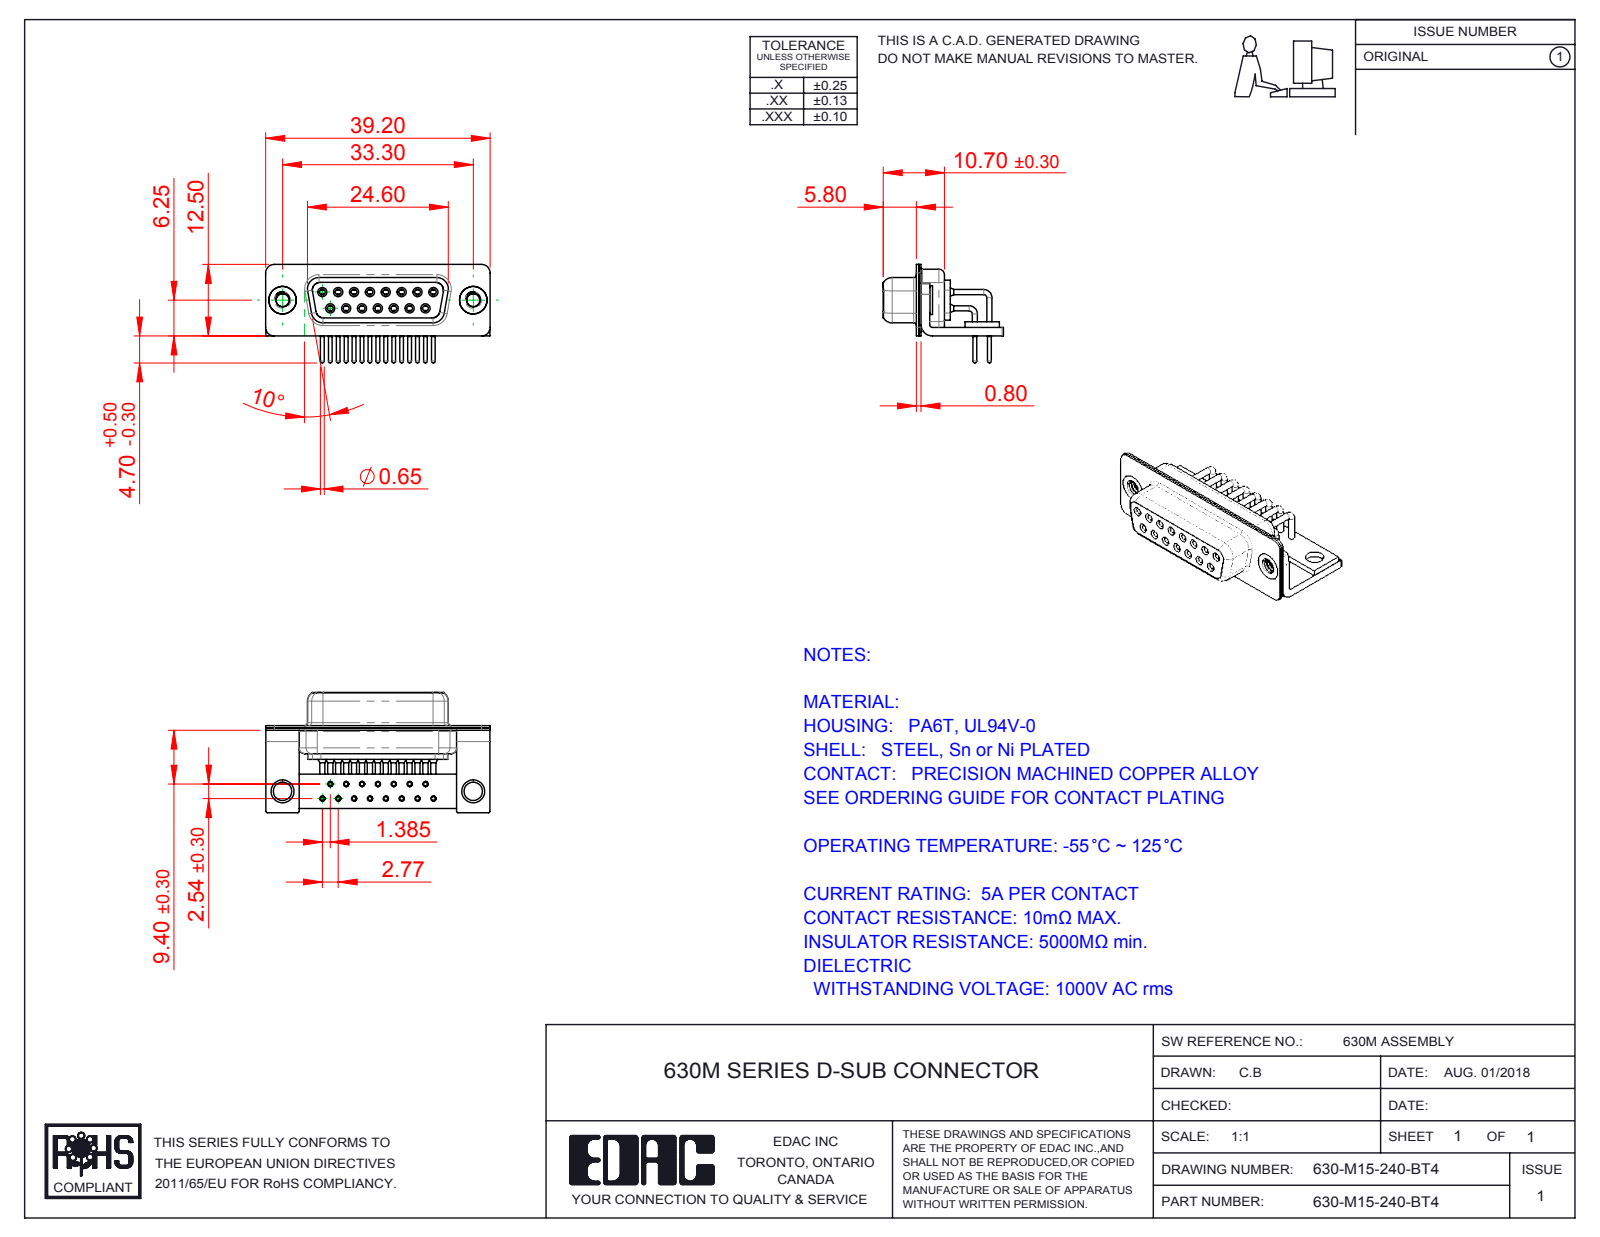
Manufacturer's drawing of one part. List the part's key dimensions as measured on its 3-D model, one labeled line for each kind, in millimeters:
Part name (STEP PRODUCT): 630M Shell Rear_15 Contacts; 630M Stabilizer Board_15 Contacts; 630M Shell Front_15 Contacts; 630-M15-240-BT4 (+5 more)
STEP written by: SolidWorks 2016 (CONFIG_CONTROL_DESIGN)
Units: millimetres
Bodies: 23 solids, 1154 faces (318 planar, 534 cylindrical, 302 other)
Overall size (bounding box): 39.2 × 21 × 17.2
Volume: 3 044 mm³ · Surface area: 7 715 mm²
Round holes (diameter × count): ⌀0.9 ×15, ⌀1 ×15, ⌀1.1 ×15, ⌀1.7 ×15, ⌀1.8 ×15, ⌀2 ×15, ⌀2.26 ×2, ⌀3.2 ×2, ⌀4 ×2, ⌀4.8 ×2
Round bosses / shafts (diameter × count): ⌀0.9 ×27, ⌀1.6 ×15, ⌀1.5 ×15, ⌀0.65 ×15, ⌀5 ×2, ⌀4.9 ×2
Partial cylindrical surfaces — rounded edges, fillets, slot ends (radius × count): R0.25 ×16, R1.5 ×16, R2 ×13, R1.35 ×8, R1.6 ×8, R0.5 ×5, R0.6 ×4, R0.65 ×4
Main face-to-face distances: 0.4, 0.8, 2.3, 9.35, 1.9, 1.5, 1, 1.45, 8.95, 0.85
Hole centre spacings: 2.77, 5.54, 8.31, 3.16, 4.87, 11.08, 2.89, 7.37
